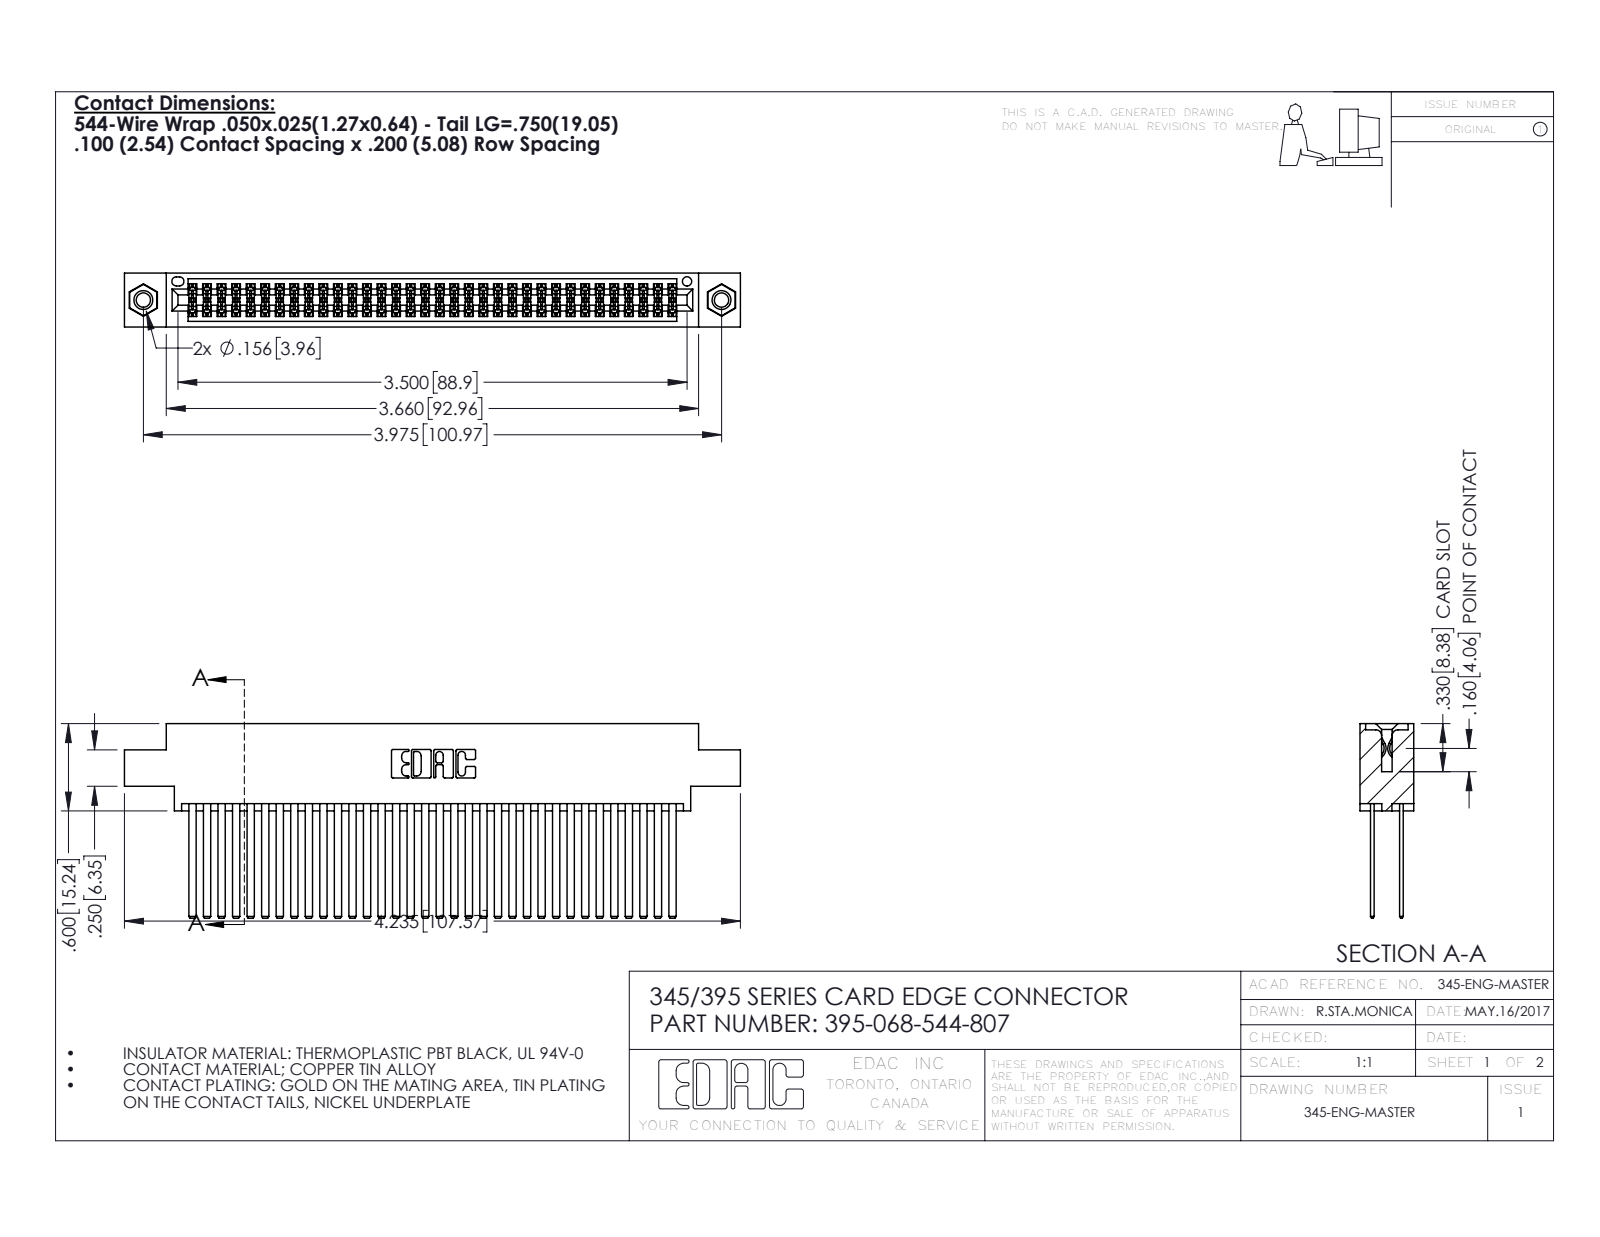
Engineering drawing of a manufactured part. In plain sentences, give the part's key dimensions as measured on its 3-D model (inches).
The part is named "345 Part_0.170 Offset - 0.156 Dia-TI; 345-292-001_345-293-144; 395-068-544-807; 345-250-001_345-250-005-103". Its 3-D file was written by "SolidWorks 2016 (CONFIG_CONTROL_DESIGN)". It is 71 solids with 3182 faces: 2088 planar, 1078 cylindrical and 16 other. Overall it measures 4.235 by 1.337 by 0.37 inches. Its volume is 0.684 cubic inches and its surface area 30.02 square inches. Round holes: 2 of diameter 0.098, 2 of diameter 0.125, 2 of diameter 0.156, 1 of diameter 0.064. Round bosses or shafts: 2 of diameter 0.155. Partial cylindrical surfaces (rounded edges, fillets, slot ends): 102 of radius 0.006, 22 of radius 0.01, 6 of radius 0.007, 6 of radius 0.031, 3 of radius 0.026, 2 of radius 0.014, 2 of radius 0.019, 2 of radius 0.022. The main face-to-face distances are 0.2, 0.025, 0.072, 0.098, 0.272, 0.298, 0.225, 0.175, 0.37, 0.15. The hole center spacings are 0.27, 3.74, 3.975.
